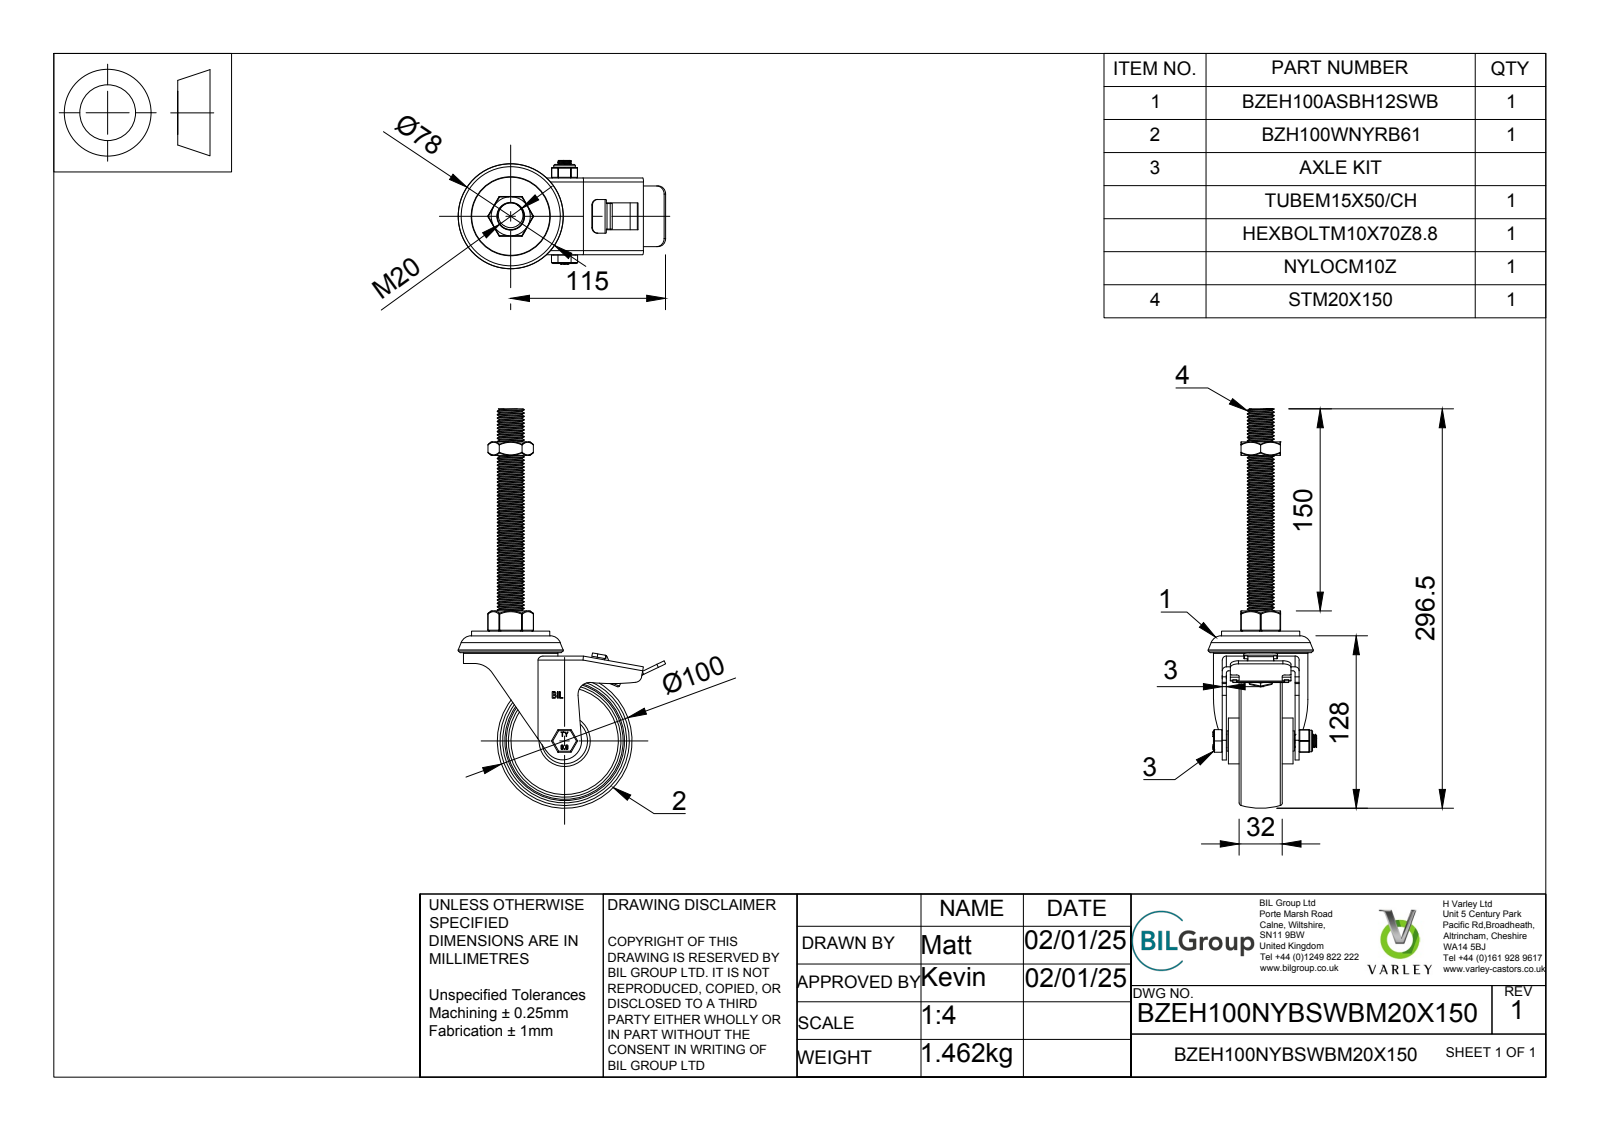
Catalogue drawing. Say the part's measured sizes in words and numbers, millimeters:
The part is named "BZEH100NYBSWBM20X150 v4; BZEH100ASBH12SWB v1; ZINC PLATED, PRESSED STEEL TOP HEAD; ZINC PLATED, PRESSED STEEL FORKS (+8 more)". Its 3-D file was written by "Autodesk Translation Framework v13.20.0.188 (AP242_MANAGED_MODEL_BASED_3D_ENGINEERING_MIM_LF)". It is 28 solids with 931 faces: 365 planar, 382 cylindrical and 184 other. Overall it measures 296.5 by 154 by 80.5 millimeters. Its volume is 293 232 cubic millimeters and its surface area 152 983 square millimeters. Round holes: 1 of diameter 8, 1 of diameter 10, 1 of diameter 10.2, 1 of diameter 10.5, 1 of diameter 12, 1 of diameter 12.2, 1 of diameter 13, 1 of diameter 14.5, 1 of diameter 15, 1 of diameter 15.2, 1 of diameter 20, 1 of diameter 21. Round bosses or shafts: 8 of diameter 4, 1 of diameter 70, 1 of diameter 58, 1 of diameter 53.5, 1 of diameter 34, 1 of diameter 28.75, 1 of diameter 25, 1 of diameter 23.5. Partial cylindrical surfaces (rounded edges, fillets, slot ends): 36 of radius 0.75, 20 of radius 0.5, 8 of radius 1, 6 of radius 1.5, 4 of radius 3, 3 of radius 2, 3 of radius 4, 2 of radius 1.76. The main face-to-face distances are 3, 8, 21.5, 29.5, 24.5, 32.5, 54, 2.5, 2, 5.5.
